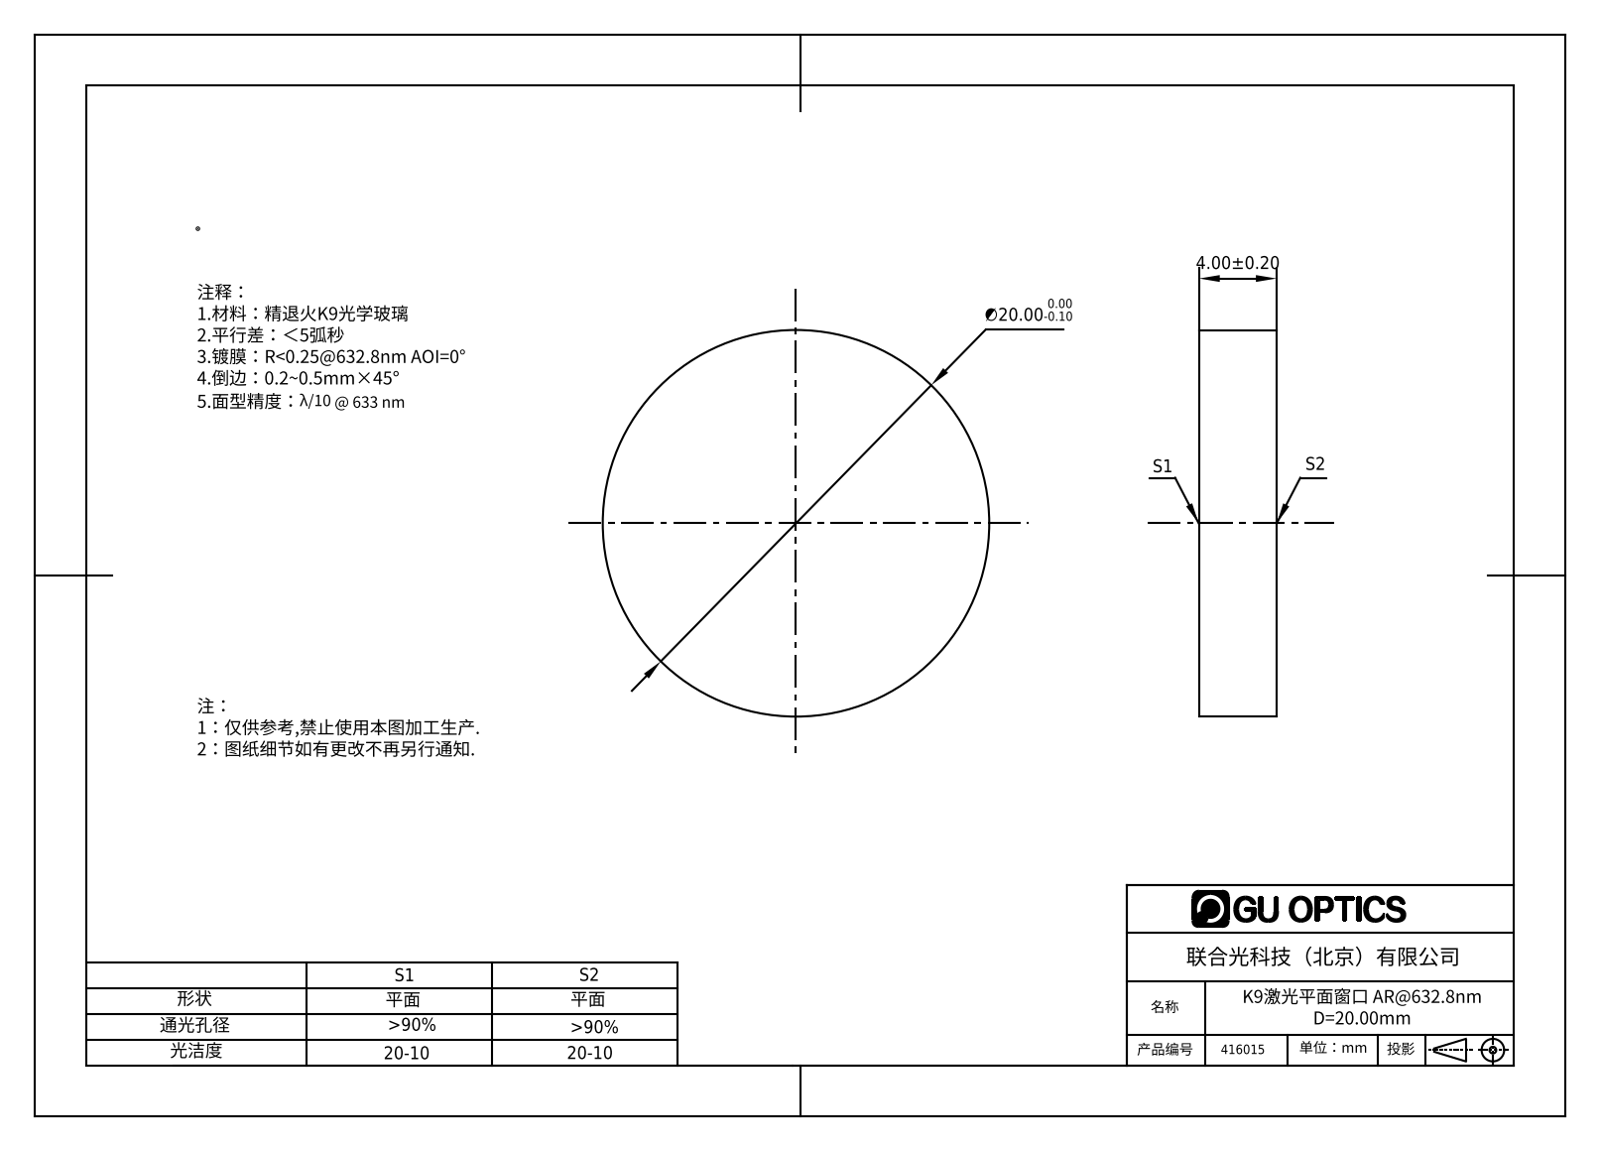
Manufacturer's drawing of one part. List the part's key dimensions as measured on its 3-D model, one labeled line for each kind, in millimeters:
Part name (STEP PRODUCT): 416004
STEP written by: SolidWorks 2016 (CONFIG_CONTROL_DESIGN)
Units: millimetres
Bodies: 1 solid, 4 faces (2 planar, 2 cylindrical, 0 other)
Overall size (bounding box): 20 × 20 × 4
Volume: 1 257 mm³ · Surface area: 880 mm²
Round bosses / shafts (diameter × count): ⌀20 ×1
Main face-to-face distances: 4
